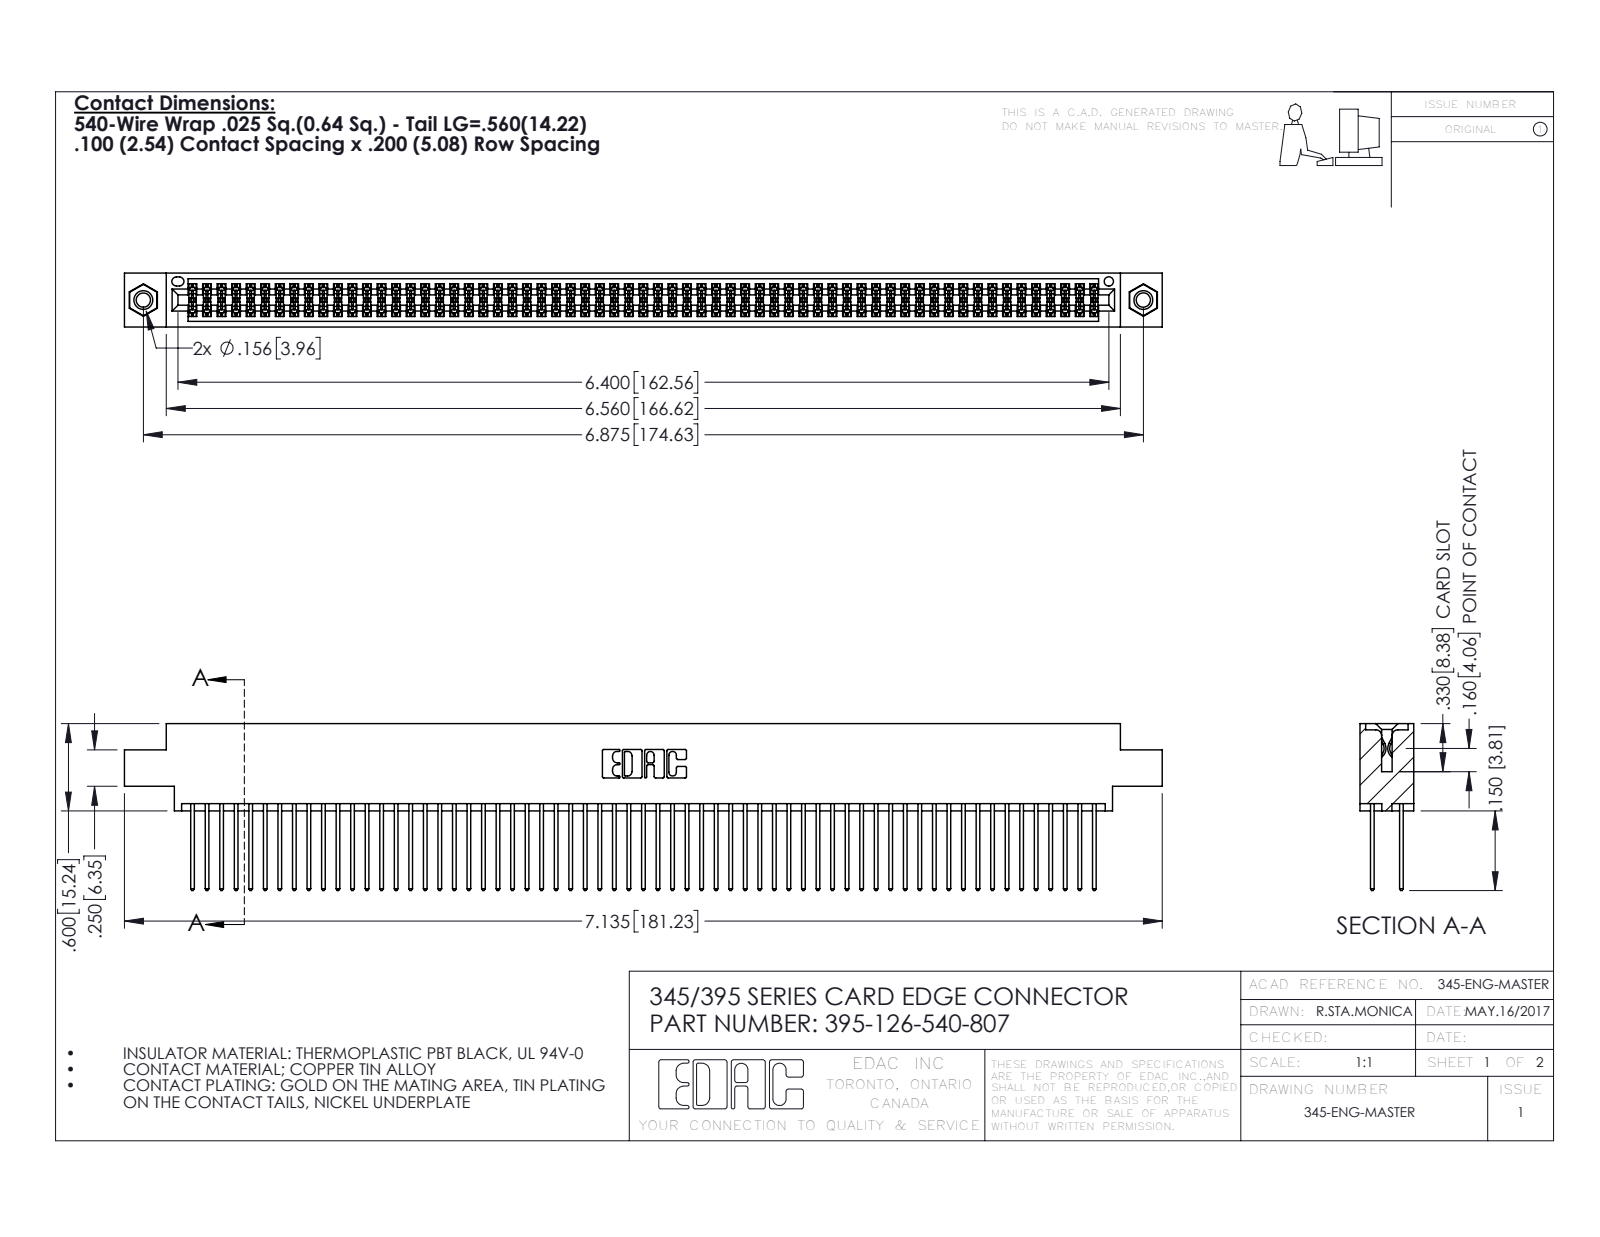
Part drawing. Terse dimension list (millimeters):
name: 345-292-001_345-293-140; 345-250-001_345-250-005-103; 395-126-540-807; 345 Part_0.170 Offset - 0.156 Dia-TI
written by: SolidWorks 2016 (CONFIG_CONTROL_DESIGN)
unit: mm
bodies: 129 solids, 6490 faces (4274 planar, 2200 cylindrical, 16 other)
size: 181.2 × 29.1 × 9.4
volume: 18 160 mm³; area: 29 630 mm²
holes: 2× ⌀2.5, 2× ⌀3.2, 2× ⌀4, 1× ⌀1.6
bosses: 2× ⌀3.9
rounds: 189× R0.2, 126× R0.3, 22× R0.3, 6× R0.2, 6× R0.8, 3× R0.7, 2× R0.4, 2× R0.5
face distances: 1.8, 7.6, 5.1, 2.5, 6.9, 0.6, 9.4, 5.7, 4.4, 3.8
hole spacings: 6.9, 168.6, 174.6
